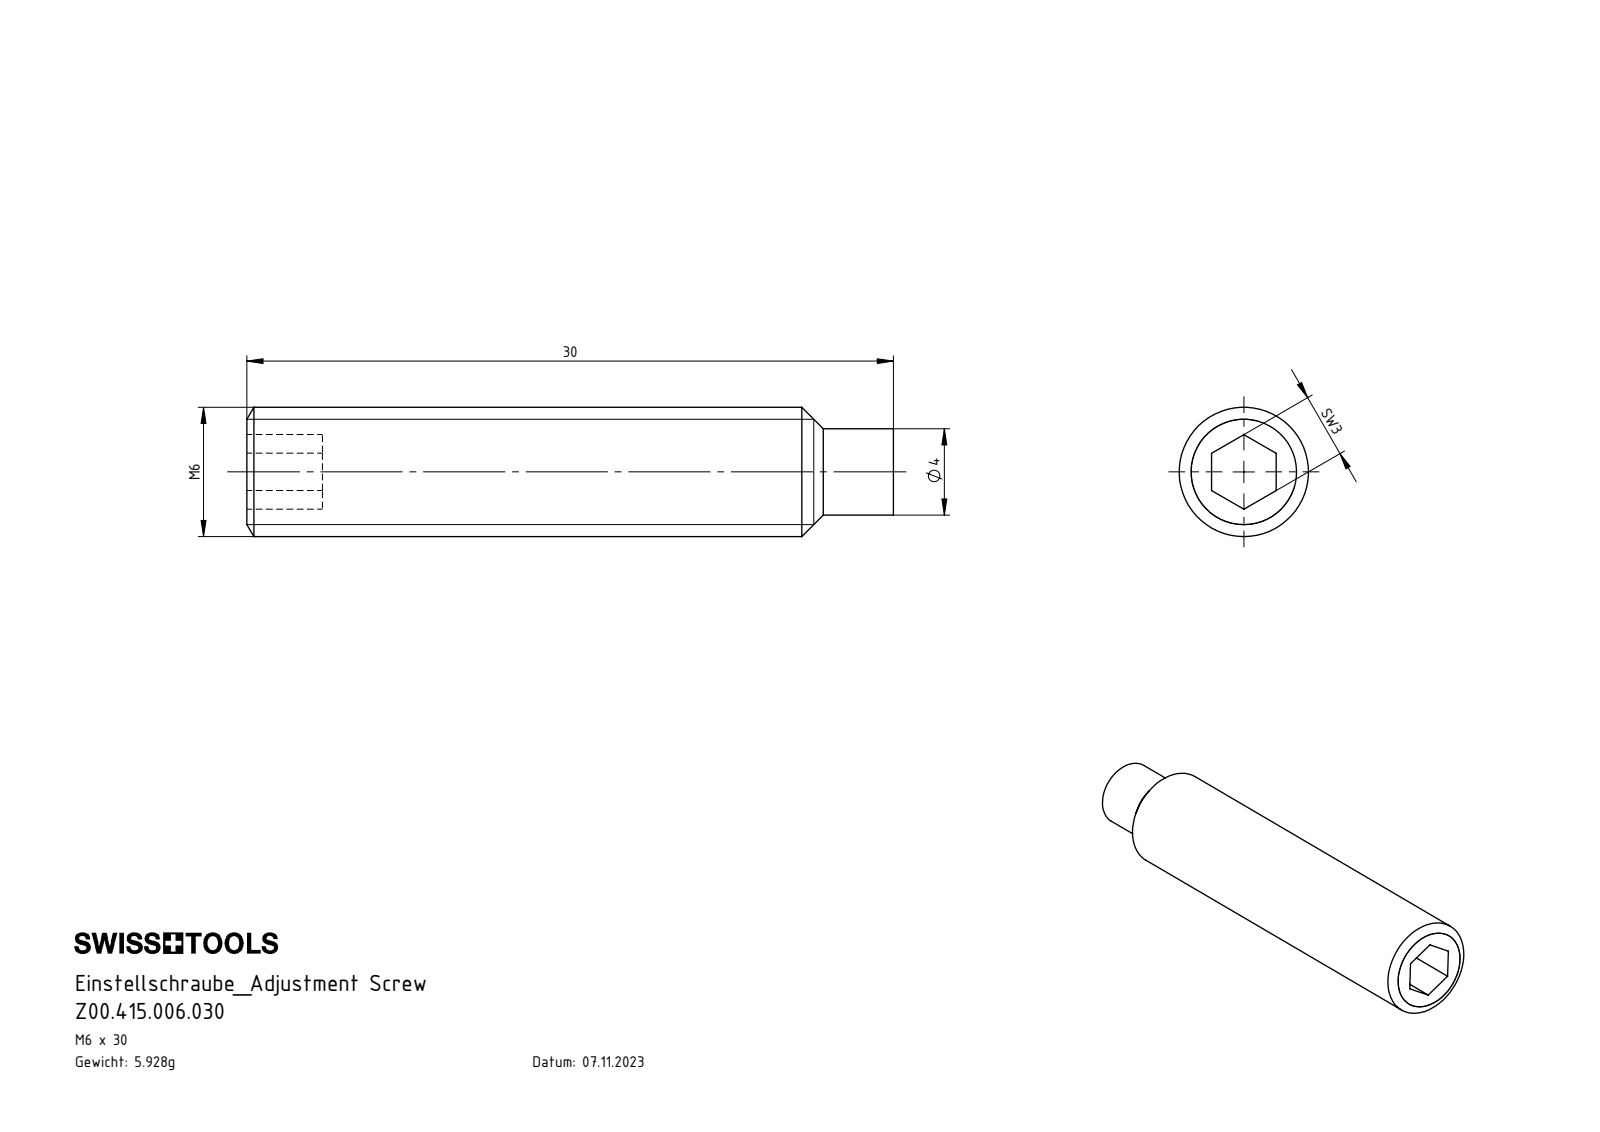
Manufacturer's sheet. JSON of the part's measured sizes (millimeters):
{"part_name": "Z00.415.006.030", "step_written_by": "SolidWorks 2022 (AUTOMOTIVE_DESIGN)", "units": "millimeters", "bodies": {"solids": 1, "faces": 17, "planar": 9, "cylindrical": 4, "other": 4}, "overall_size": [30, 6, 6], "volume_mm3": 760, "surface_area_mm2": 621, "round_bosses_or_shafts": [[6, 1], [4, 1]], "face_to_face_distances": [3, 30, 3.5, 26.5]}
